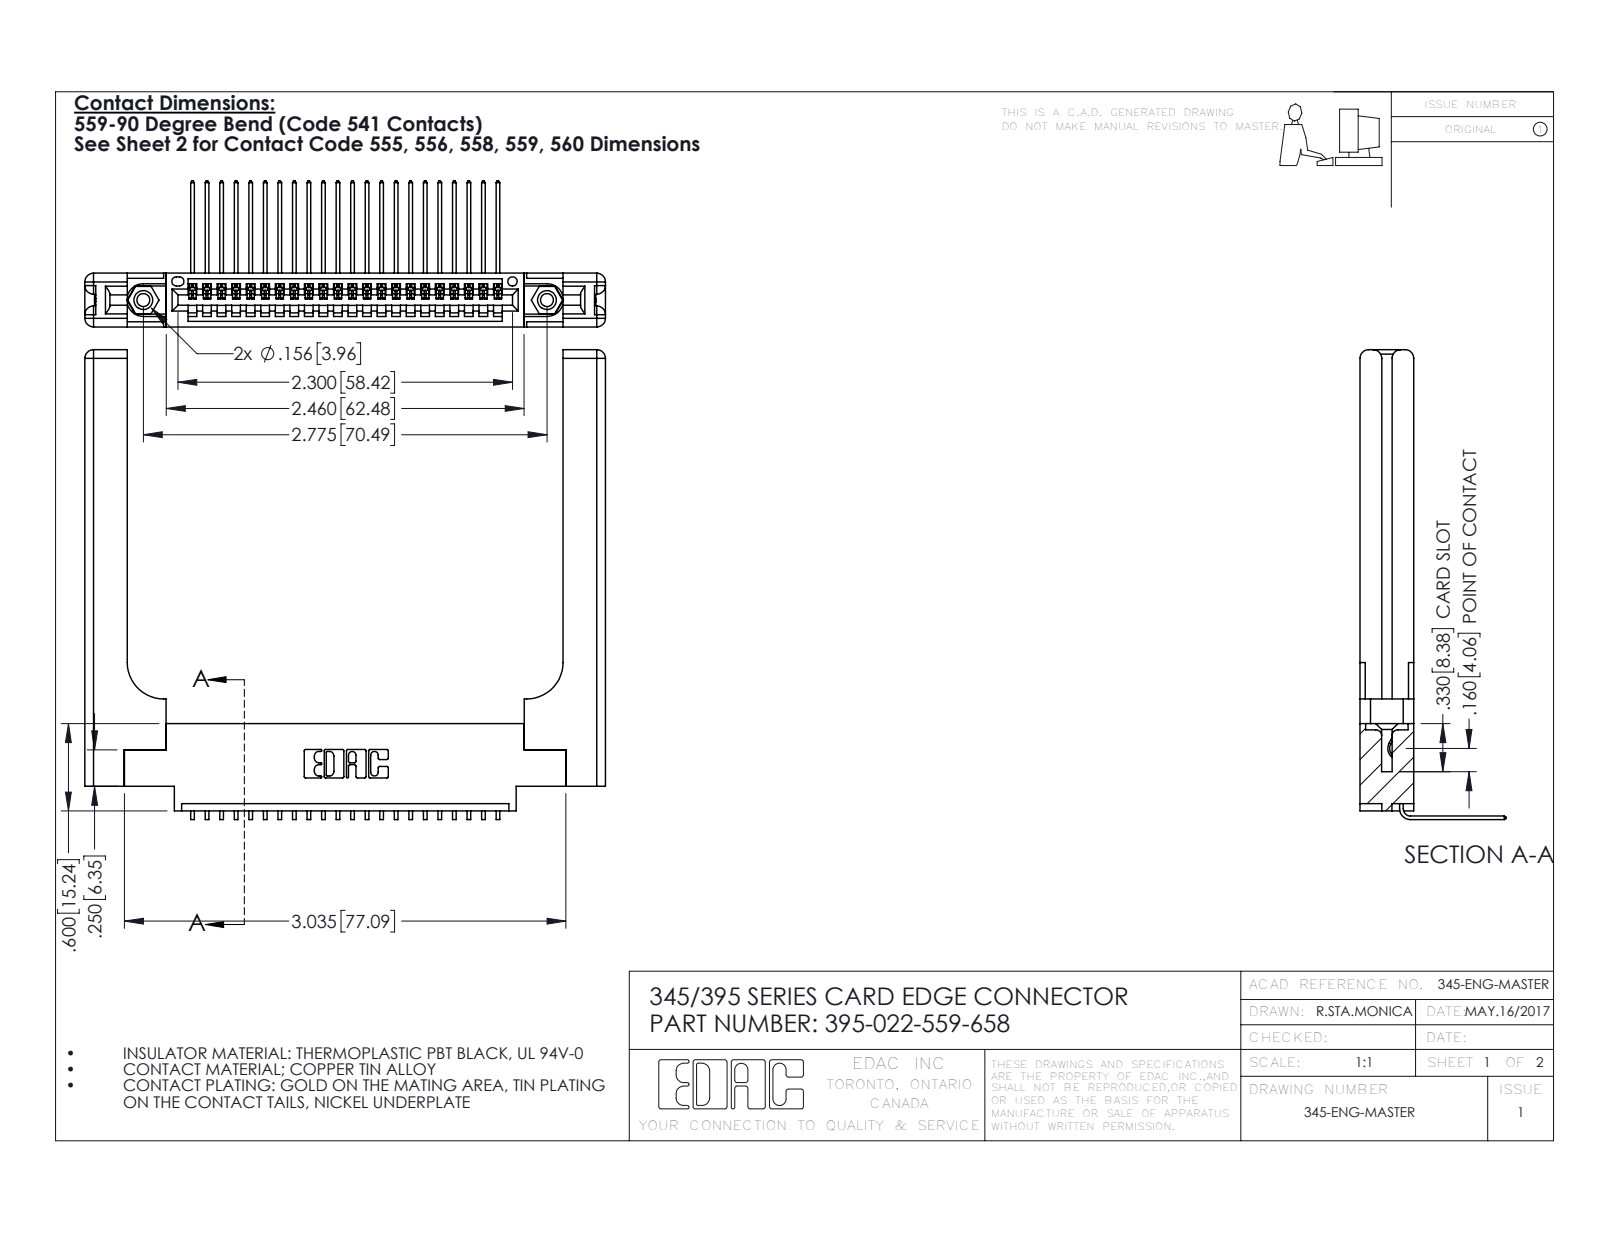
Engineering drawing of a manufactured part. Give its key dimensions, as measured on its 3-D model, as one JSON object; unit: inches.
{"part_name": "345-220-058_345-220-058; 345-250-001_345-250-001-102; 395-022-559-658; 345-292-001_558 559 Tail - 1 (+1 more)", "step_written_by": "SolidWorks 2016 (CONFIG_CONTROL_DESIGN)", "units": "inches", "bodies": {"solids": 27, "faces": 1706, "planar": 1156, "cylindrical": 490, "other": 60}, "overall_size": [3.579, 3.229, 1.005], "volume_in3": 1.033, "surface_area_in2": 26.03, "round_holes": [[0.089, 2], [0.125, 2], [0.156, 2], [0.064, 1]], "round_bosses_or_shafts": [[0.155, 2]], "partial_cylinders_radius": [[0.006, 44], [0.01, 22], [0.06, 16], [0.007, 6], [0.031, 6], [0.026, 3], [0.03, 2], [0.031, 2]], "face_to_face_distances": [0.37, 0.072, 0.298, 0.15, 0.148, 0.077, 0.22, 0.098, 0.272, 0.025], "hole_center_spacings": [0.27, 2.541, 2.775]}
